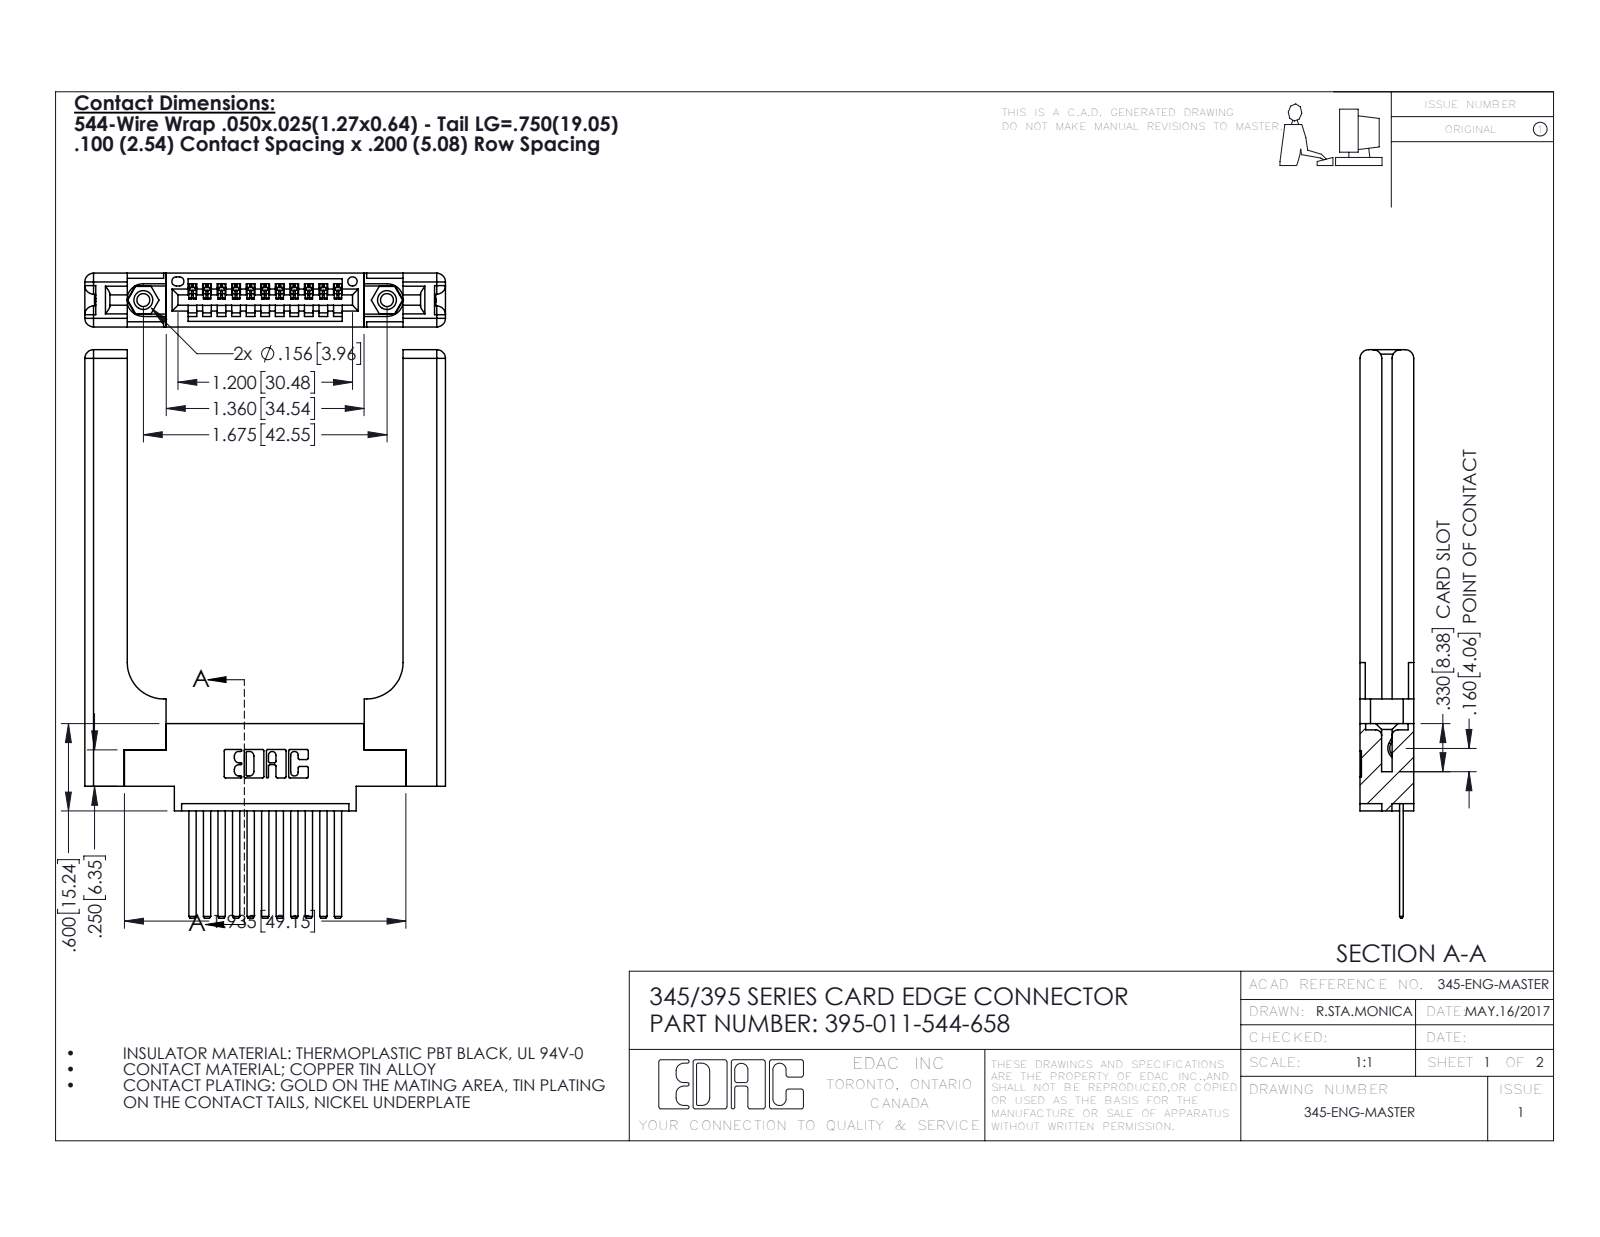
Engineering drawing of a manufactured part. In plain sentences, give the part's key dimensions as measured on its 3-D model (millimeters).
The part is named "345-220-058_345-220-058; 395-011-544-658; 345-292-001_345-293-144; 345 Part_0.170 Offset - 0.156 Dia-TH (+1 more)". Its 3-D file was written by "SolidWorks 2016 (CONFIG_CONTROL_DESIGN)". It is 16 solids with 958 faces: 628 planar, 270 cylindrical and 60 other. Overall it measures 99.2 by 63 by 9.4 millimeters. Its volume is 14 200 cubic millimeters and its surface area 13 020 square millimeters. Round holes: 2 of diameter 2.3, 2 of diameter 3.2, 2 of diameter 4, 1 of diameter 1.6. Round bosses or shafts: 2 of diameter 3.9. Partial cylindrical surfaces (rounded edges, fillets, slot ends): 22 of radius 0.2, 22 of radius 0.3, 16 of radius 1.5, 6 of radius 0.2, 6 of radius 0.8, 3 of radius 0.7, 2 of radius 0.8, 2 of radius 0.8. The main face-to-face distances are 9.4, 1.8, 7.6, 3.8, 5.6, 3.8, 2, 2.5, 6.9, 0.6. The hole center spacings are 6.9, 36.7, 42.5.
